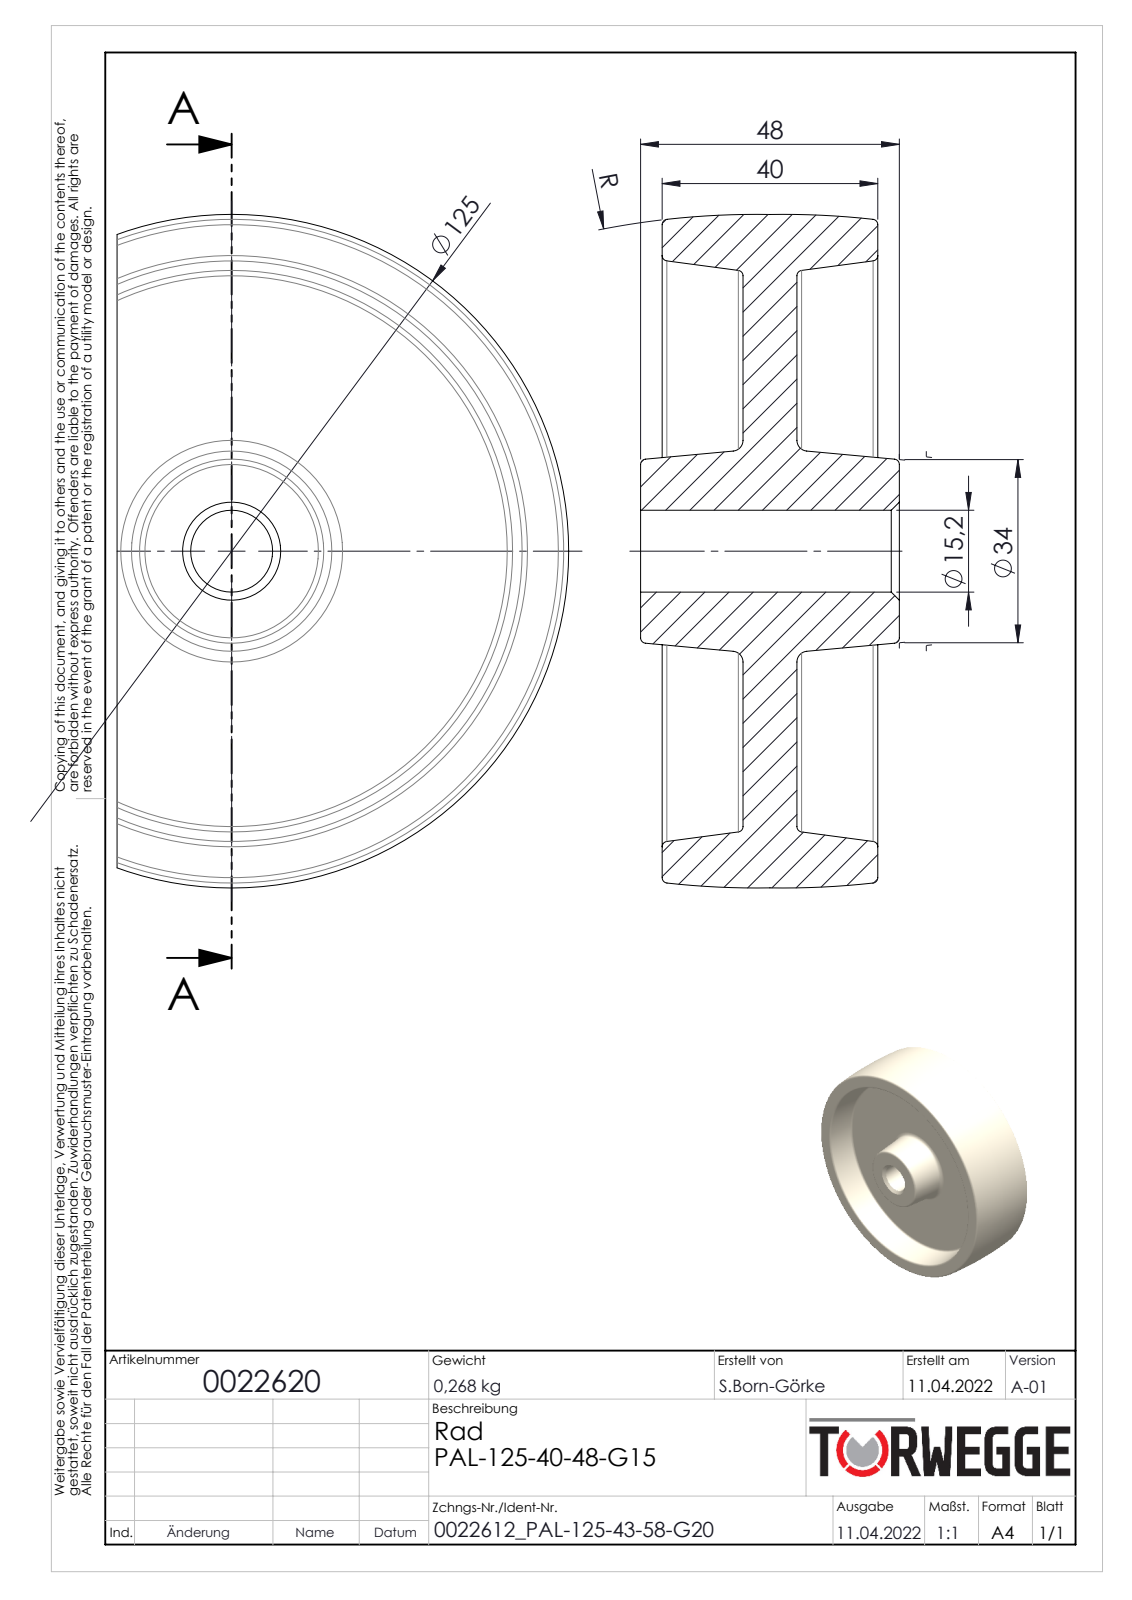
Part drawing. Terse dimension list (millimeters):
name: 0022620
written by: SolidWorks 2020 (AUTOMOTIVE_DESIGN)
unit: mm
bodies: 1 solid, 42 faces (6 planar, 2 cylindrical, 34 other)
size: 125.04 × 125.04 × 48
volume: 251 182 mm³; area: 53 059 mm²
holes: 1× ⌀15.2
face distances: 10, 15, 25, 40, 4, 19, 29, 44, 48
